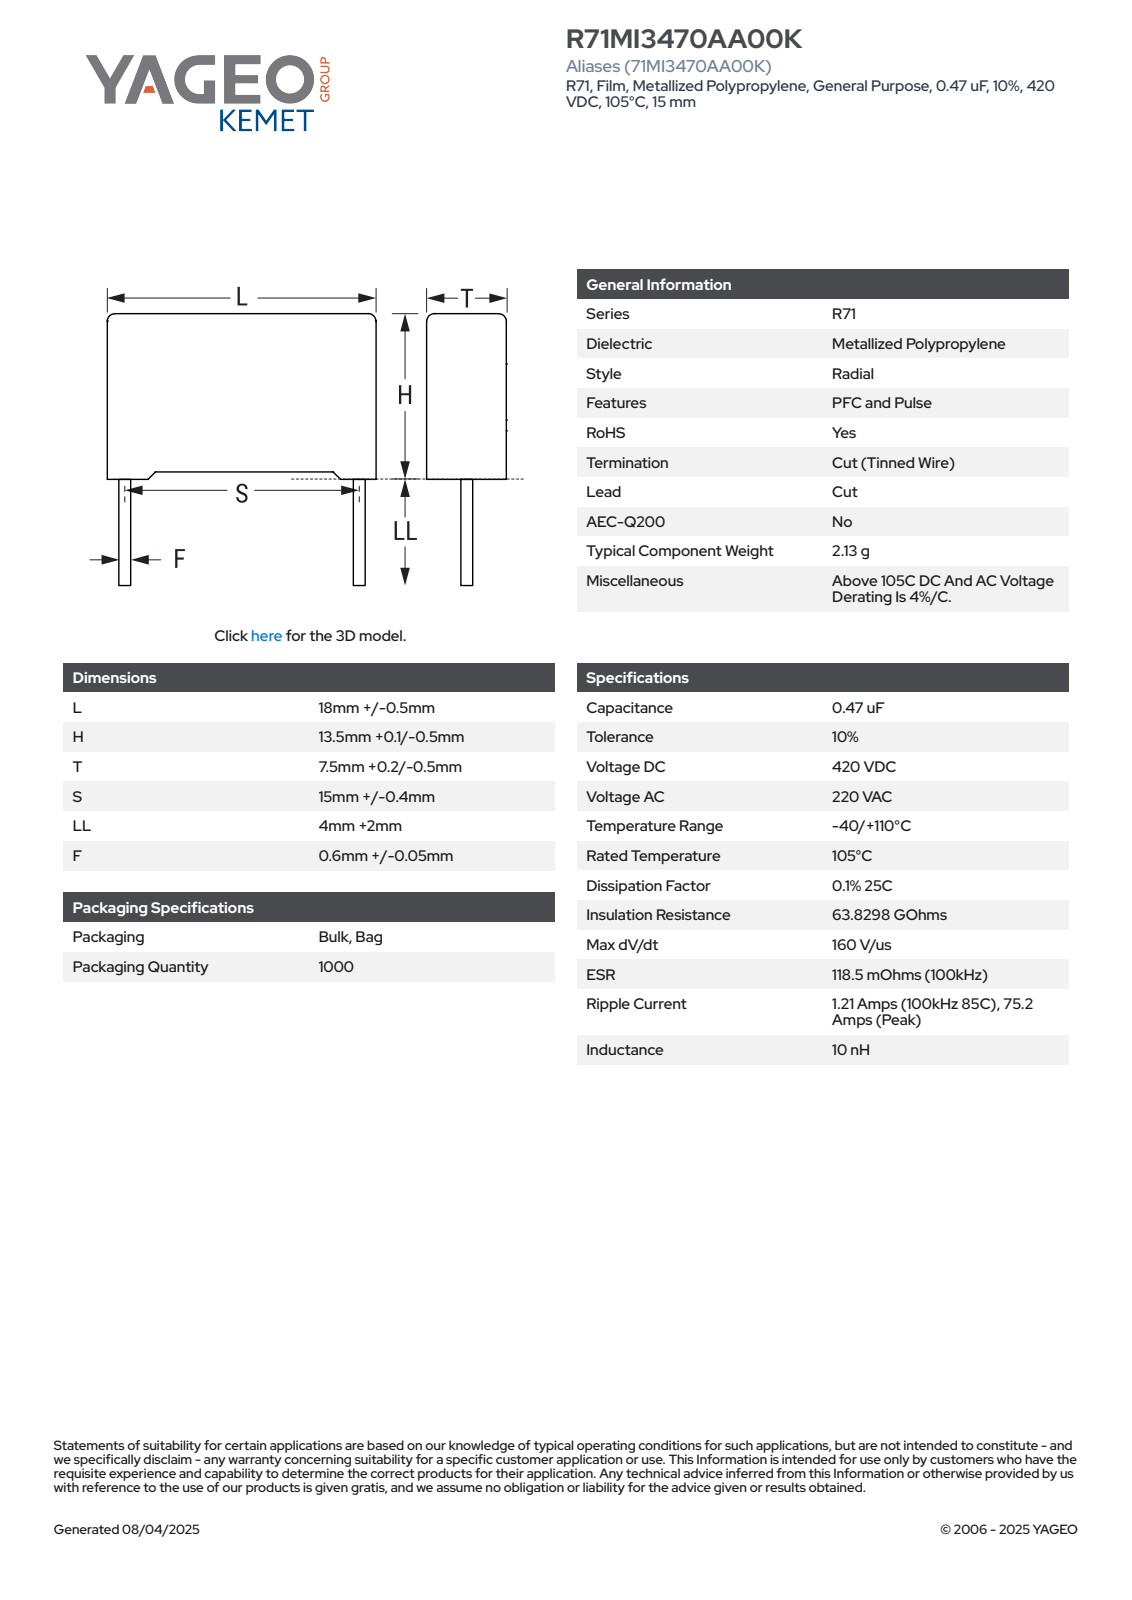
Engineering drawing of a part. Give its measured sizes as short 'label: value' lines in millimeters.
name: CFR_RB2_18X13.5X7.5_L18.5H13.6T7.7S15LL6F0.65
written by: SolidWorks 2021 (AUTOMOTIVE_DESIGN)
unit: mm
bodies: 4 solids, 85 faces (77 planar, 8 cylindrical, 0 other)
size: 19.6 × 18.5 × 7.71
volume: 1 849 mm³; area: 1 054 mm²
bosses: 2× ⌀0.65
rounds: 4× R0.5
face distances: 7.7, 12.85, 18.5, 0.62, 0.75, 13.6, 7.08, 0.47, 13.13, 17.88
